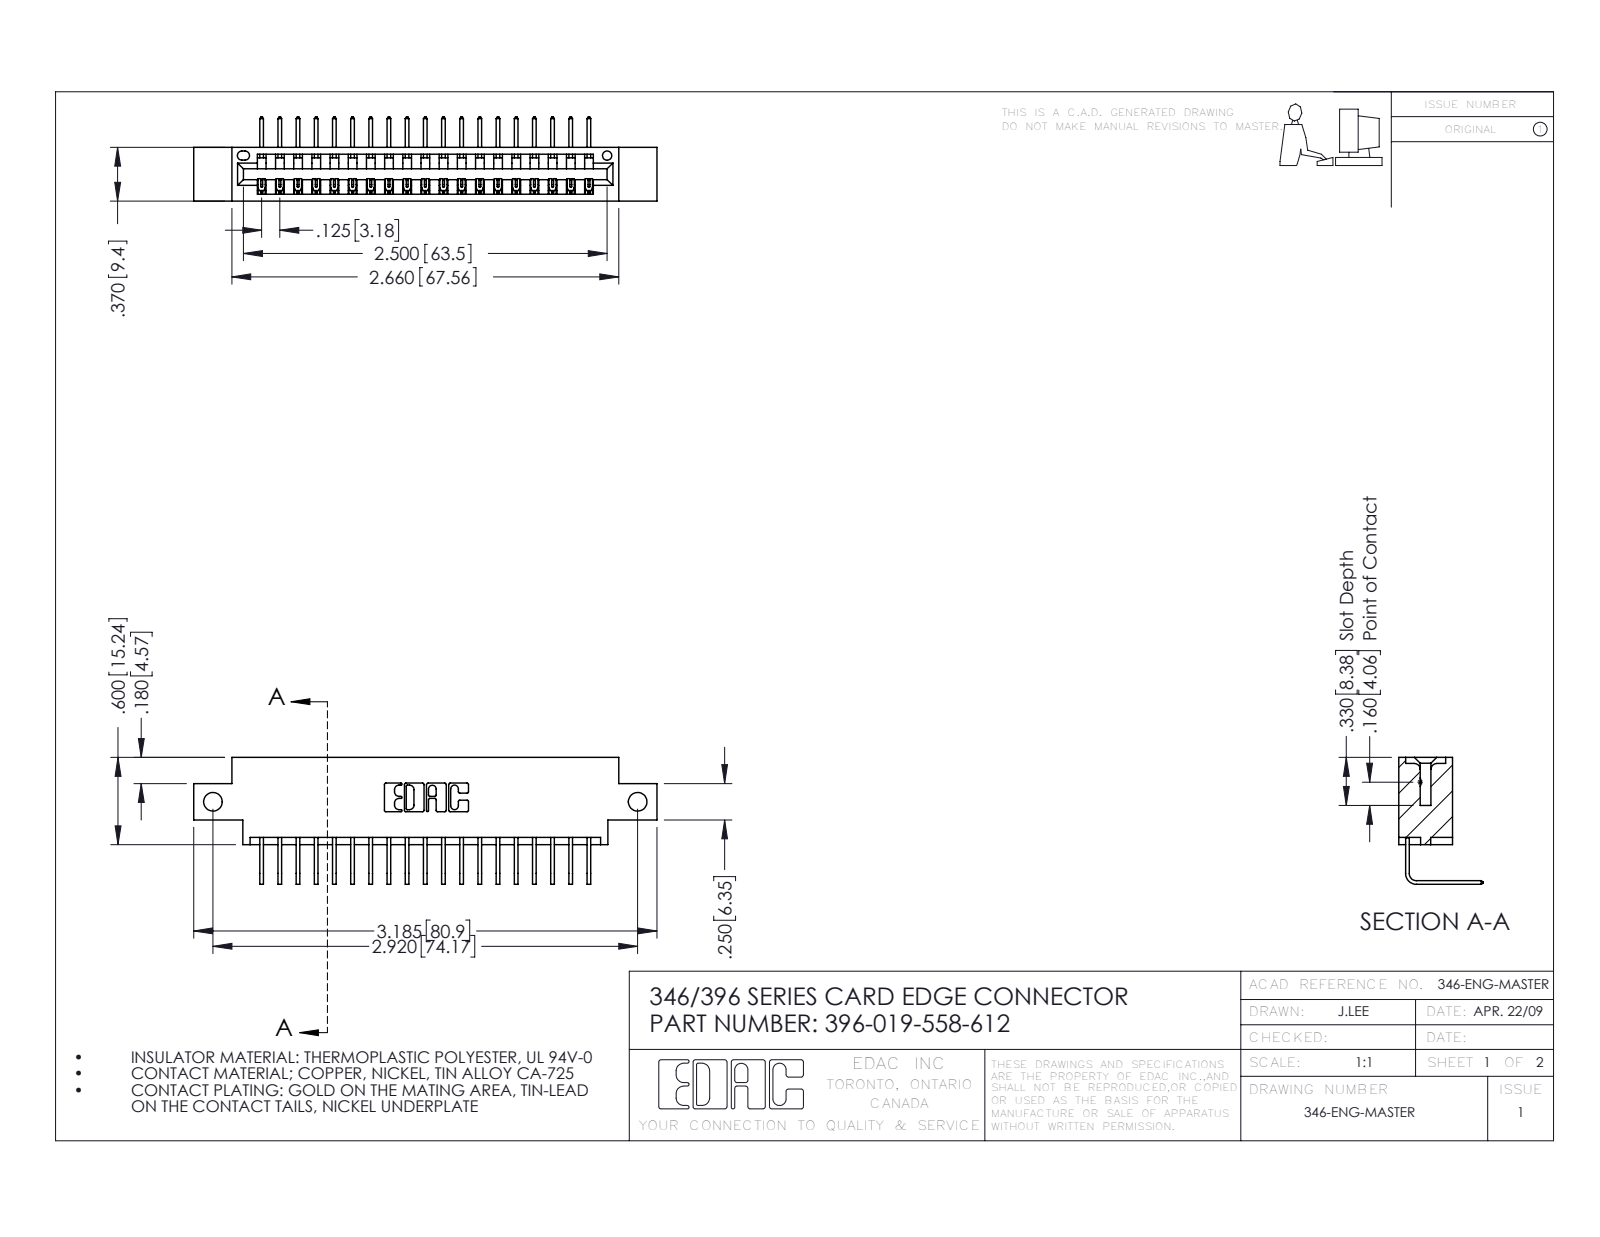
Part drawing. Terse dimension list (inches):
name: 346 Part_0.170 Offset - Side Mount; 345-292-001_558 Tail - 2; 396-019-558-612
written by: SolidWorks 2016 (CONFIG_CONTROL_DESIGN)
unit: in
bodies: 20 solids, 1266 faces (878 planar, 388 cylindrical, 0 other)
size: 3.185 × 0.873 × 0.58
volume: 0.452 in³; area: 14.57 in²
holes: 2× ⌀0.128, 1× ⌀0.064
rounds: 38× R0.006, 22× R0.01, 6× R0.007, 6× R0.031, 3× R0.026, 2× R0.031, 2× R0.04, 1× R0.014
face distances: 0.322, 0.048, 0.37, 0.25, 0.298, 0.025, 0.072, 0.148, 0.222, 0.1
hole spacings: 2.92
